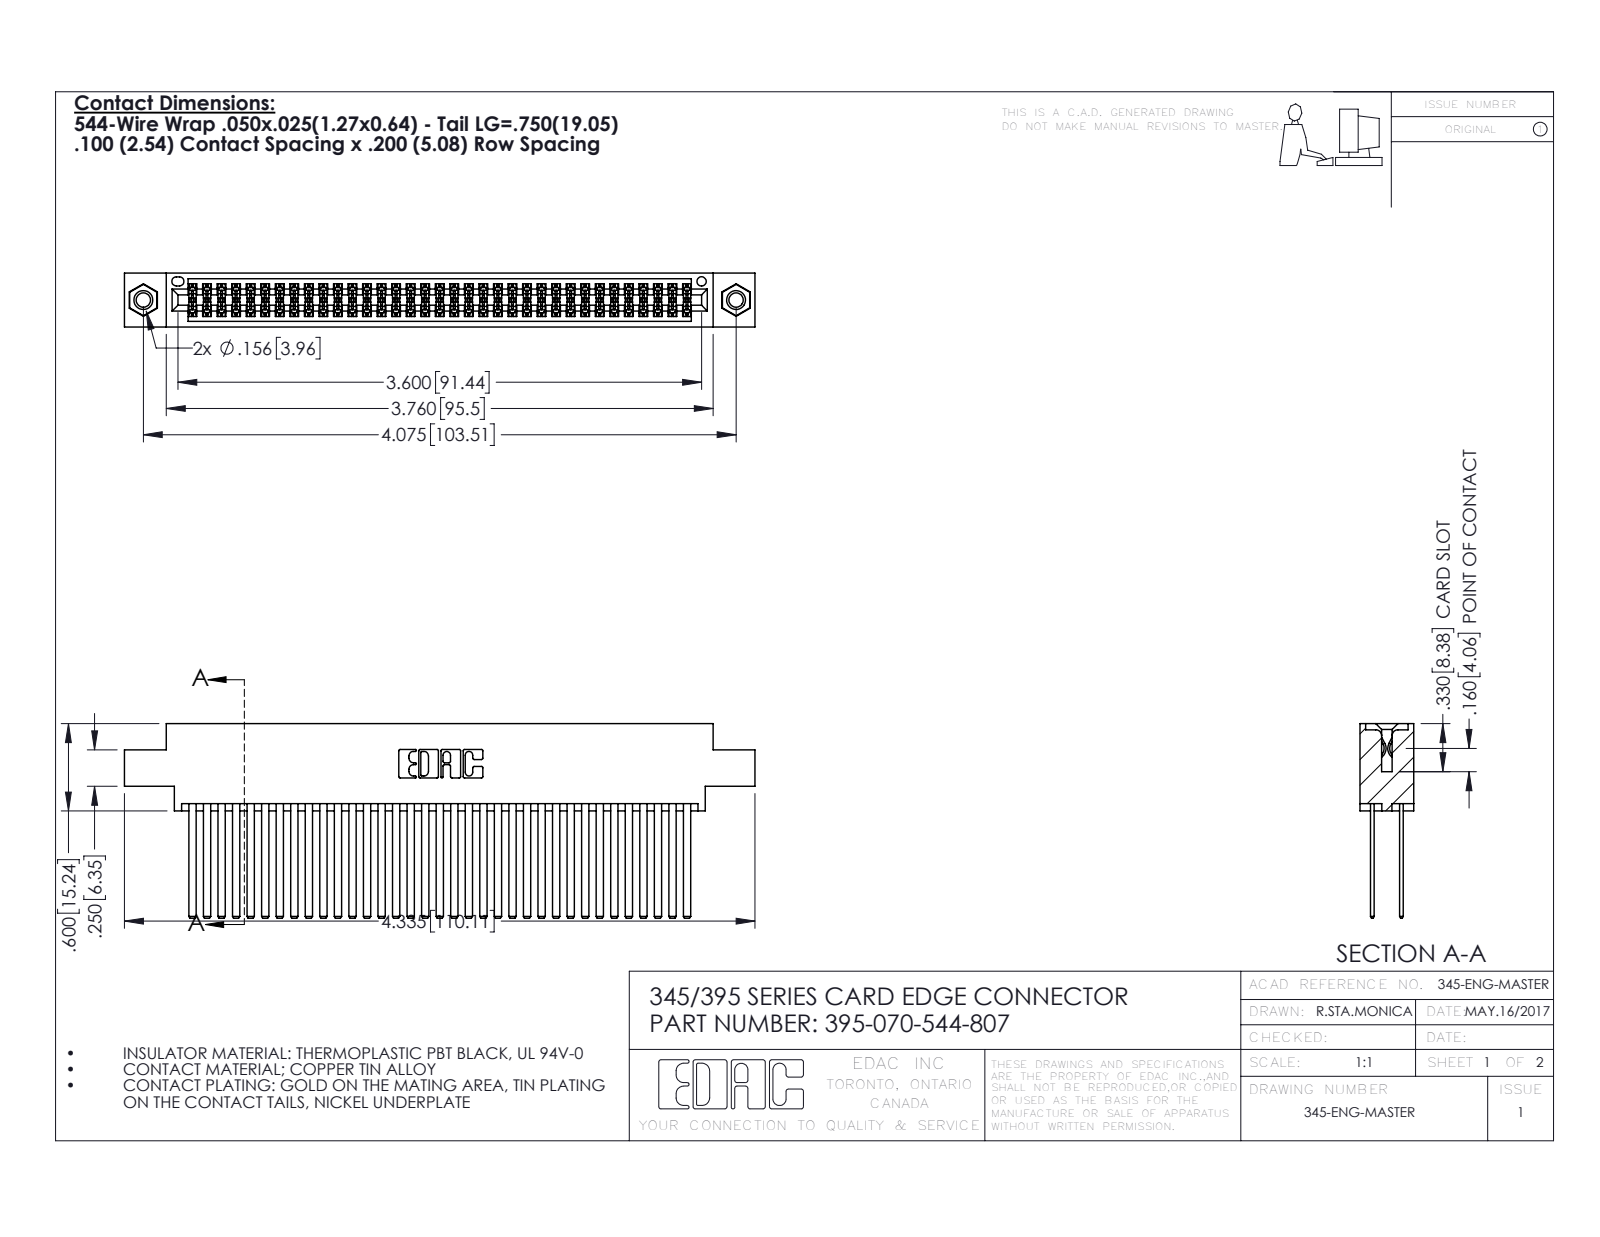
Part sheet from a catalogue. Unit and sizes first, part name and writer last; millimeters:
Units: millimetres
Overall size (bounding box): 110.1 × 34 × 9.4
Round holes (diameter × count): ⌀2.5 ×2, ⌀3.2 ×2, ⌀4 ×2, ⌀1.6 ×1
Round bosses / shafts (diameter × count): ⌀3.9 ×2
Partial cylindrical surfaces — rounded edges, fillets, slot ends (radius × count): R0.2 ×105, R0.3 ×22, R0.2 ×6, R0.8 ×6, R0.7 ×3, R0.4 ×2, R0.5 ×2, R0.6 ×2
Main face-to-face distances: 5.1, 0.6, 1.8, 2.5, 6.9, 7.6, 5.7, 4.4, 9.4, 3.8
Hole centre spacings: 6.9, 97.5, 103.5
Volume: 11 500 mm³ · Surface area: 19 890 mm²
Bodies: 73 solids, 3270 faces (2146 planar, 1108 cylindrical, 16 other)
Part name (STEP PRODUCT): 345-250-001_345-250-005-103; 395-070-544-807; 345-292-001_345-293-144; 345 Part_0.170 Offset - 0.156 Dia-TI
STEP written by: SolidWorks 2016 (CONFIG_CONTROL_DESIGN)
